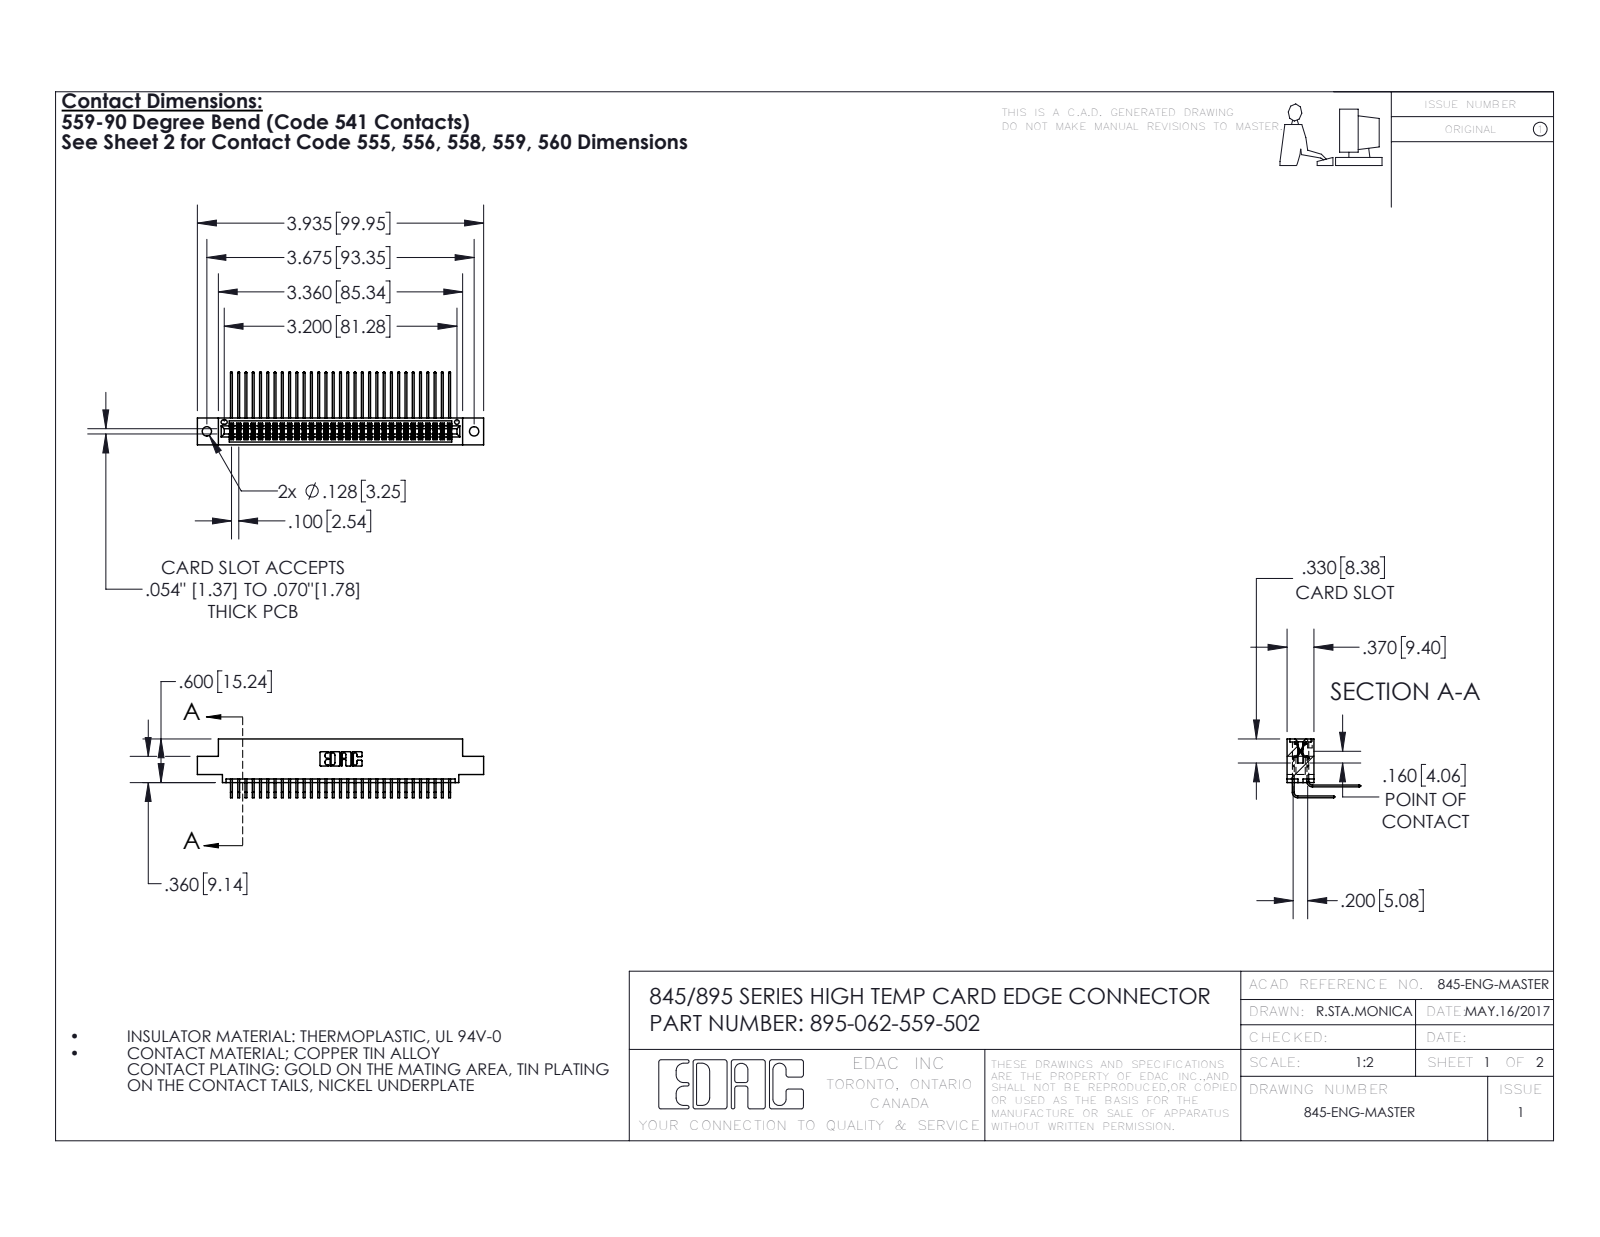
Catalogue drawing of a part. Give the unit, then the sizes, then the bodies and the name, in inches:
Units: inches
Overall size (bounding box): 3.935 × 1.005 × 0.809
Round holes (diameter × count): ⌀0.128 ×2, ⌀0.064 ×1
Partial cylindrical surfaces — rounded edges, fillets, slot ends (radius × count): R0.006 ×93, R0.01 ×22, R0.007 ×6, R0.031 ×6, R0.026 ×3, R0.014 ×2, R0.019 ×2, R0.022 ×2
Main face-to-face distances: 0.072, 0.298, 0.2, 0.37, 0.098, 0.272, 0.025, 0.225, 0.15, 0.175
Hole centre spacings: 0.27, 3.44, 3.675
Volume: 0.601 in³ · Surface area: 24.58 in²
Bodies: 63 solids, 3354 faces (2254 planar, 1100 cylindrical, 0 other)
Part name (STEP PRODUCT): 345-292-001_559 Tail - 2; 395-062-559-502; 345-292-001_558 559 Tail - 1; 345 Part_0.110 Offset - 0.128 Dia
STEP written by: SolidWorks 2016 (CONFIG_CONTROL_DESIGN)
